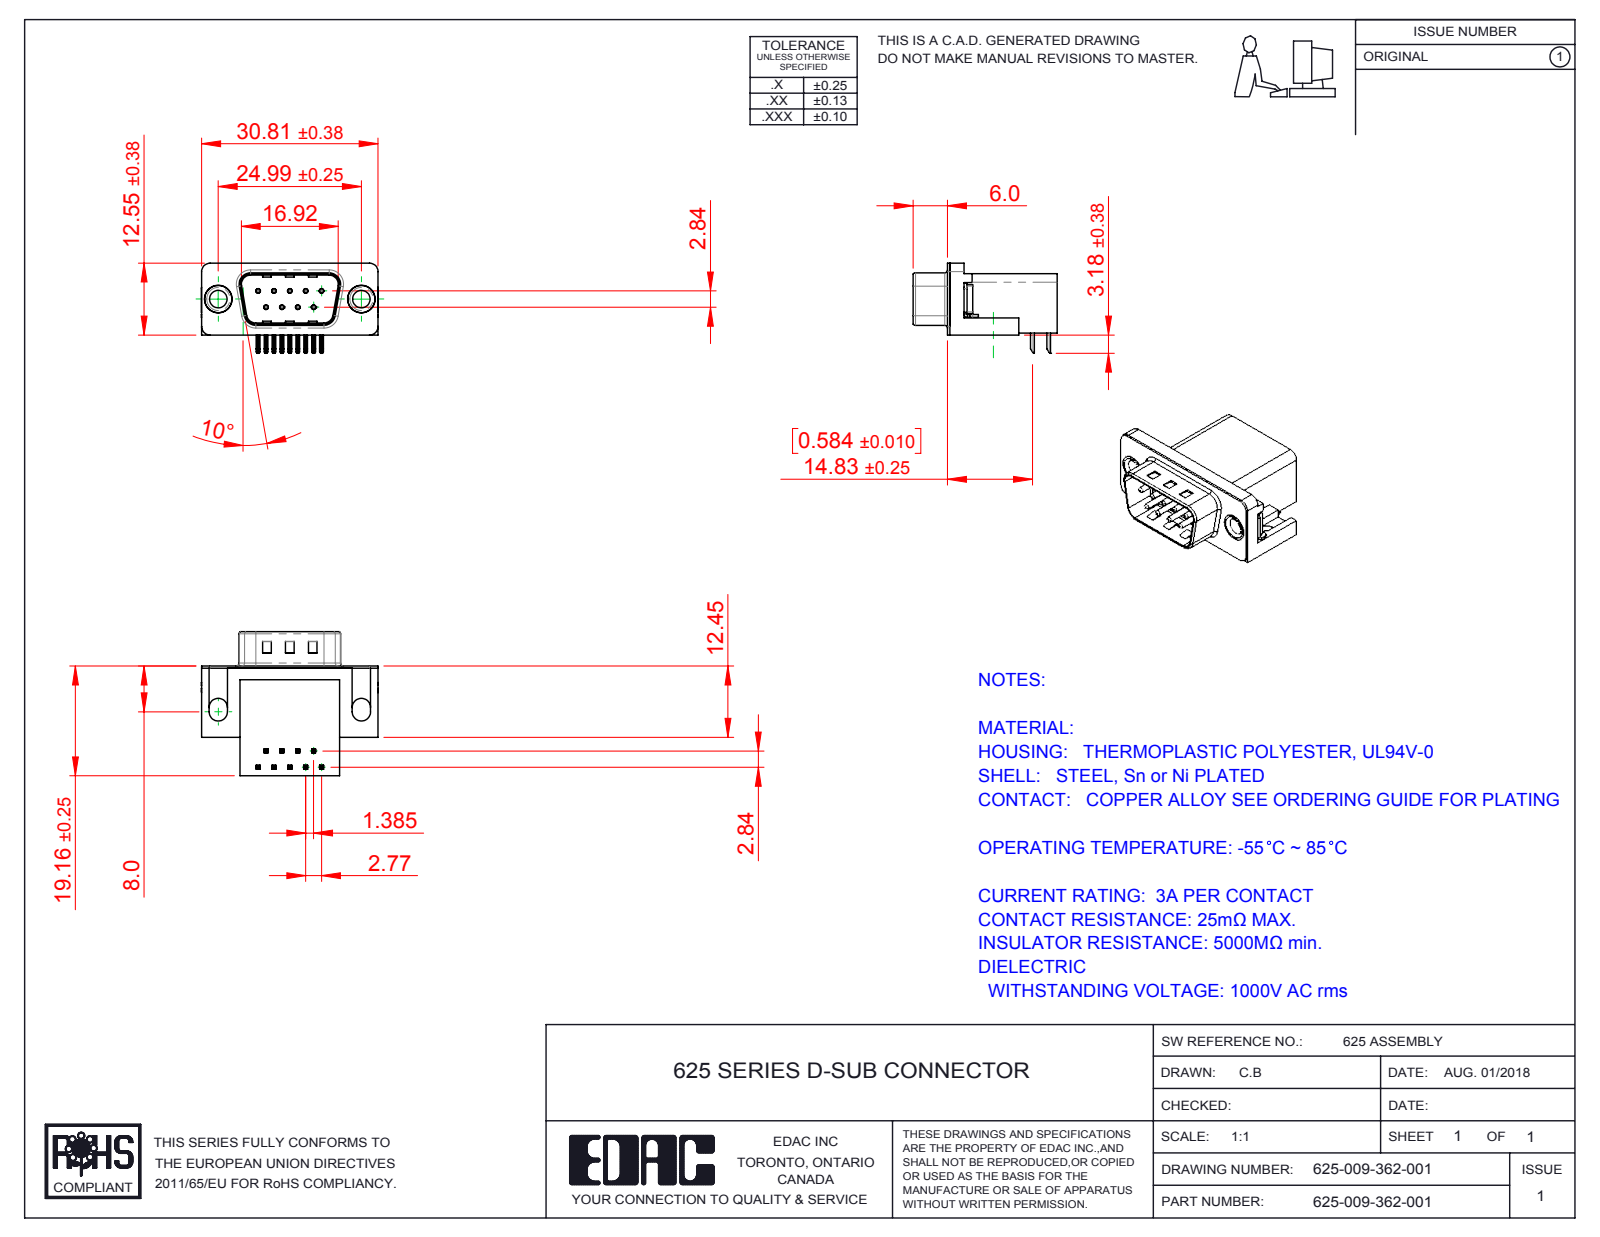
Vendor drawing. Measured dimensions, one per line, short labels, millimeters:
name: 625-009-362-001; 625 Contact Top; 625 Housing_9 Socket; 625 Thru Hole Rivet (+3 more)
written by: SolidWorks 2016 (CONFIG_CONTROL_DESIGN)
unit: mm
bodies: 15 solids, 951 faces (575 planar, 295 cylindrical, 81 other)
size: 30.89 × 25.16 × 15.73
volume: 4 436 mm³; area: 4 794 mm²
holes: 9× ⌀0.35, 9× ⌀0.8, 2× ⌀3.05, 2× ⌀4, 2× ⌀4.8, 2× ⌀5
bosses: 9× ⌀0.75, 2× ⌀4.9, 2× ⌀4.75, 2× ⌀3.85
rounds: 44× R0.25, 18× R0.12, 16× R1, 9× R0.5, 8× R1.5, 8× R1.6, 4× R0.9, 4× R2
face distances: 0.4, 10.34, 18.76, 19.16, 2.9, 16.26, 2.5, 0.35, 10.69, 6.7
hole spacings: 3.16, 2.77, 5.54, 5.03, 5.04, 8.31, 7.48, 7.49
